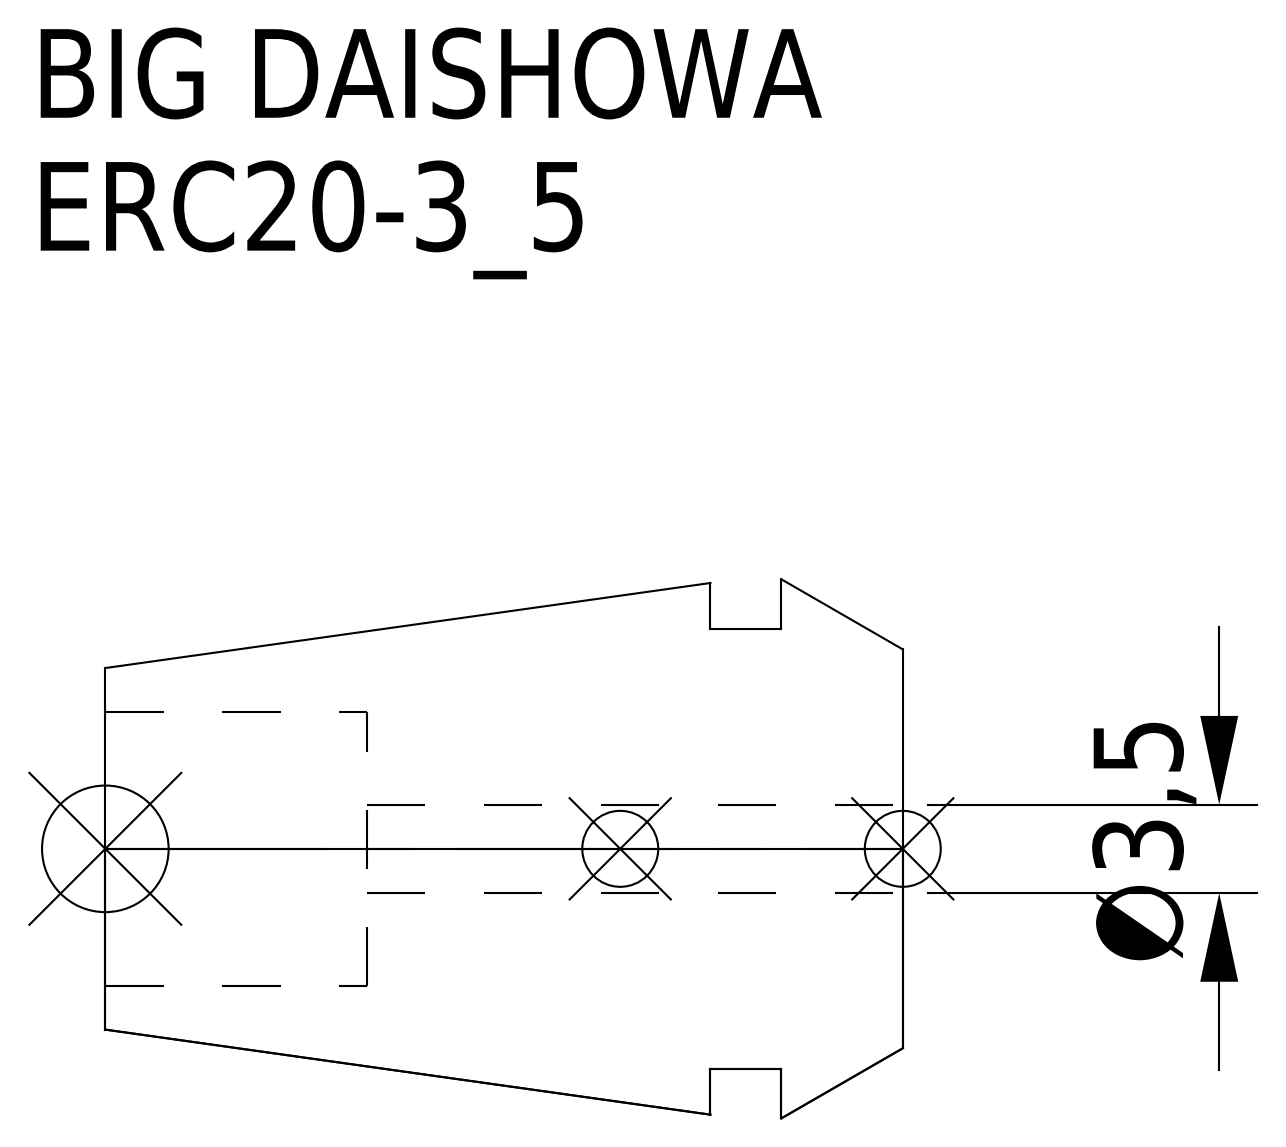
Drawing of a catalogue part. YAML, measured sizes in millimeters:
part_name: "ERC20-3_5"
step_written_by: "CREO PARAMETRIC BY PTC INC, 2016380 (AUTOMOTIVE_DESIGN)"
units: millimeters
bodies: {solids: 1, faces: 15, planar: 5, cylindrical: 6, other: 4}
overall_size: [31.5, 21.3, 21.3]
volume: 6732
surface_area: 2960
round_holes:
  - {diameter: 3.5, count: 1}
  - {diameter: 10.8, count: 1}
round_bosses_or_shafts:
  - {diameter: 17.4, count: 1}
face_to_face_distances: [4.8, 7.6, 2.8, 21.16, 16.36, 13.56, 31.5, 26.7, 23.9, 10.34]
